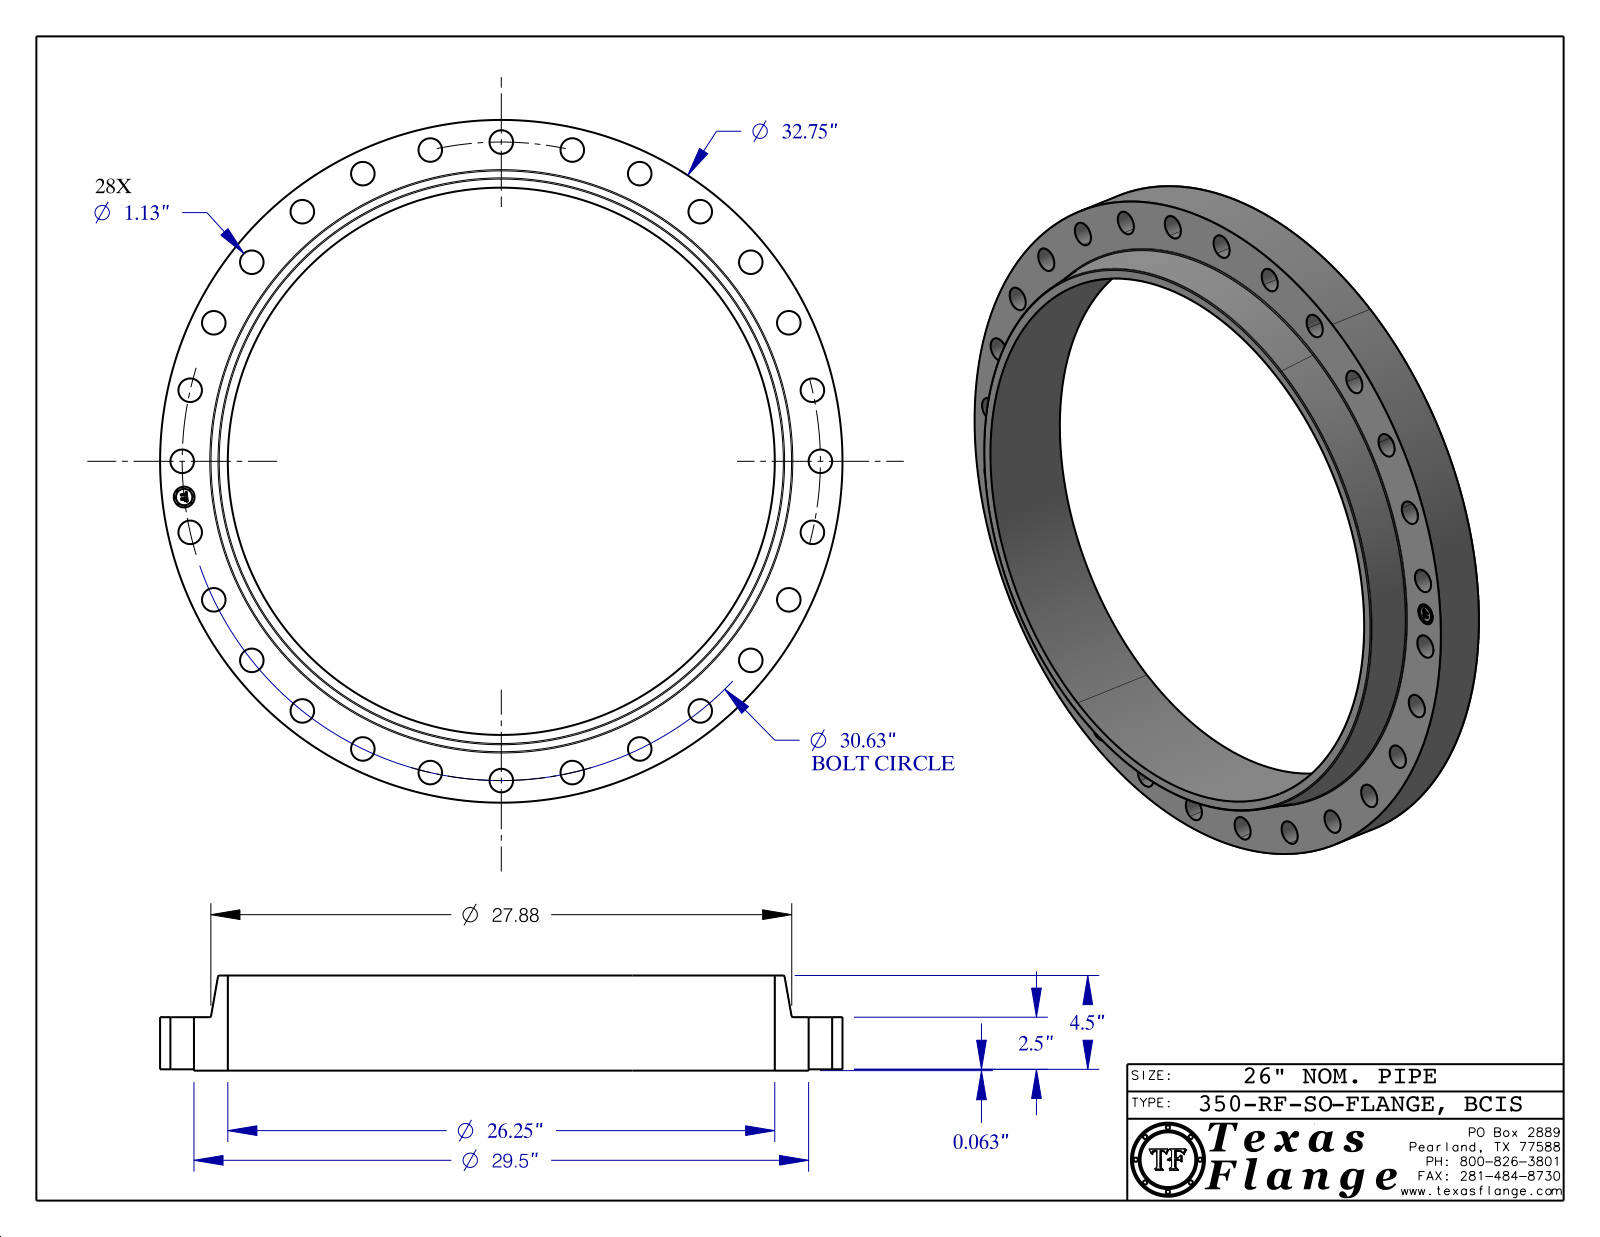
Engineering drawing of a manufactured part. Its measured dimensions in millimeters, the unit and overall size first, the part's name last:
Units: millimetres
Overall size (bounding box): 831.9 × 831.9 × 115.9
Round holes (diameter × count): ⌀28.7 ×28, ⌀25.4 ×1, ⌀666.8 ×1
Round bosses / shafts (diameter × count): ⌀1.5 ×8, ⌀831.9 ×1, ⌀749.3 ×1, ⌀20 ×1
Main face-to-face distances: 65.1, 1.6, 63.5, 115.9, 114.3, 50.8, 0.4, 64.7, 63.1, 51.2
Hole centre spacings: 257, 389, 550.1, 758.5, 773.1, 87.1, 413.9, 608.3
Volume: 13 100 000 mm³ · Surface area: 1 017 000 mm²
Bodies: 1 solid, 457 faces (369 planar, 82 cylindrical, 6 other)
Part name (STEP PRODUCT): 350-RF-SO
STEP written by: CATIA V5 STEP AP214 (AUTOMOTIVE_DESIGN)
